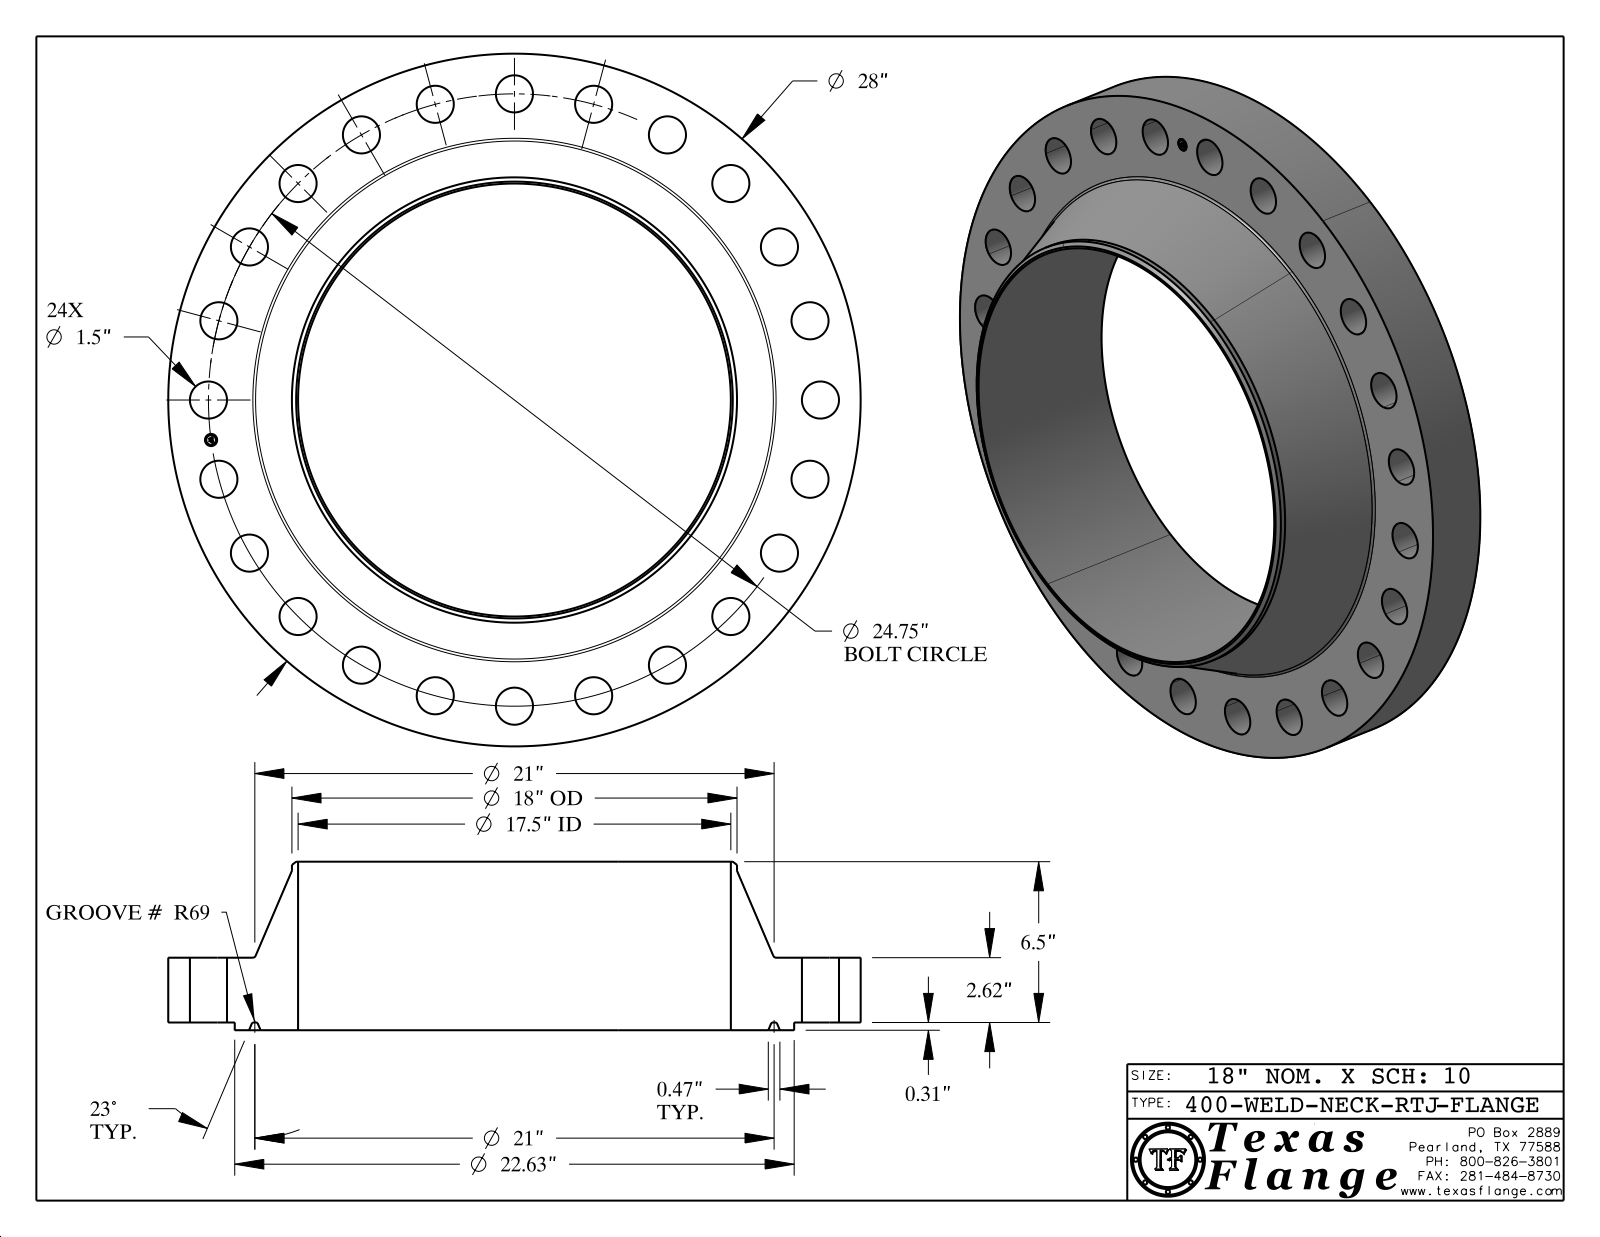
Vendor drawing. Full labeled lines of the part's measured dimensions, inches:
Part name (STEP PRODUCT): 400-WELD-NECK-RTJ
STEP written by: CATIA V5 STEP AP214 (AUTOMOTIVE_DESIGN)
Units: inches
Bodies: 1 solid, 461 faces (371 planar, 76 cylindrical, 14 other)
Overall size (bounding box): 28 × 28 × 6.813
Volume: 1 126 in³ · Surface area: 1 773 in²
Round holes (diameter × count): ⌀1.5 ×24, ⌀0.495 ×1, ⌀17.5 ×1
Round bosses / shafts (diameter × count): ⌀0.03 ×8, ⌀28 ×1, ⌀22.625 ×1, ⌀18 ×1, ⌀0.39 ×1
Main face-to-face distances: 2.62, 0.313, 2.933, 6.813, 6.5, 3.88, 2.918, 2.605, 0.015, 3.895
Hole centre spacings: 12.375, 9.471, 15.067, 17.501, 21.434, 22.866, 23.906, 3.23
